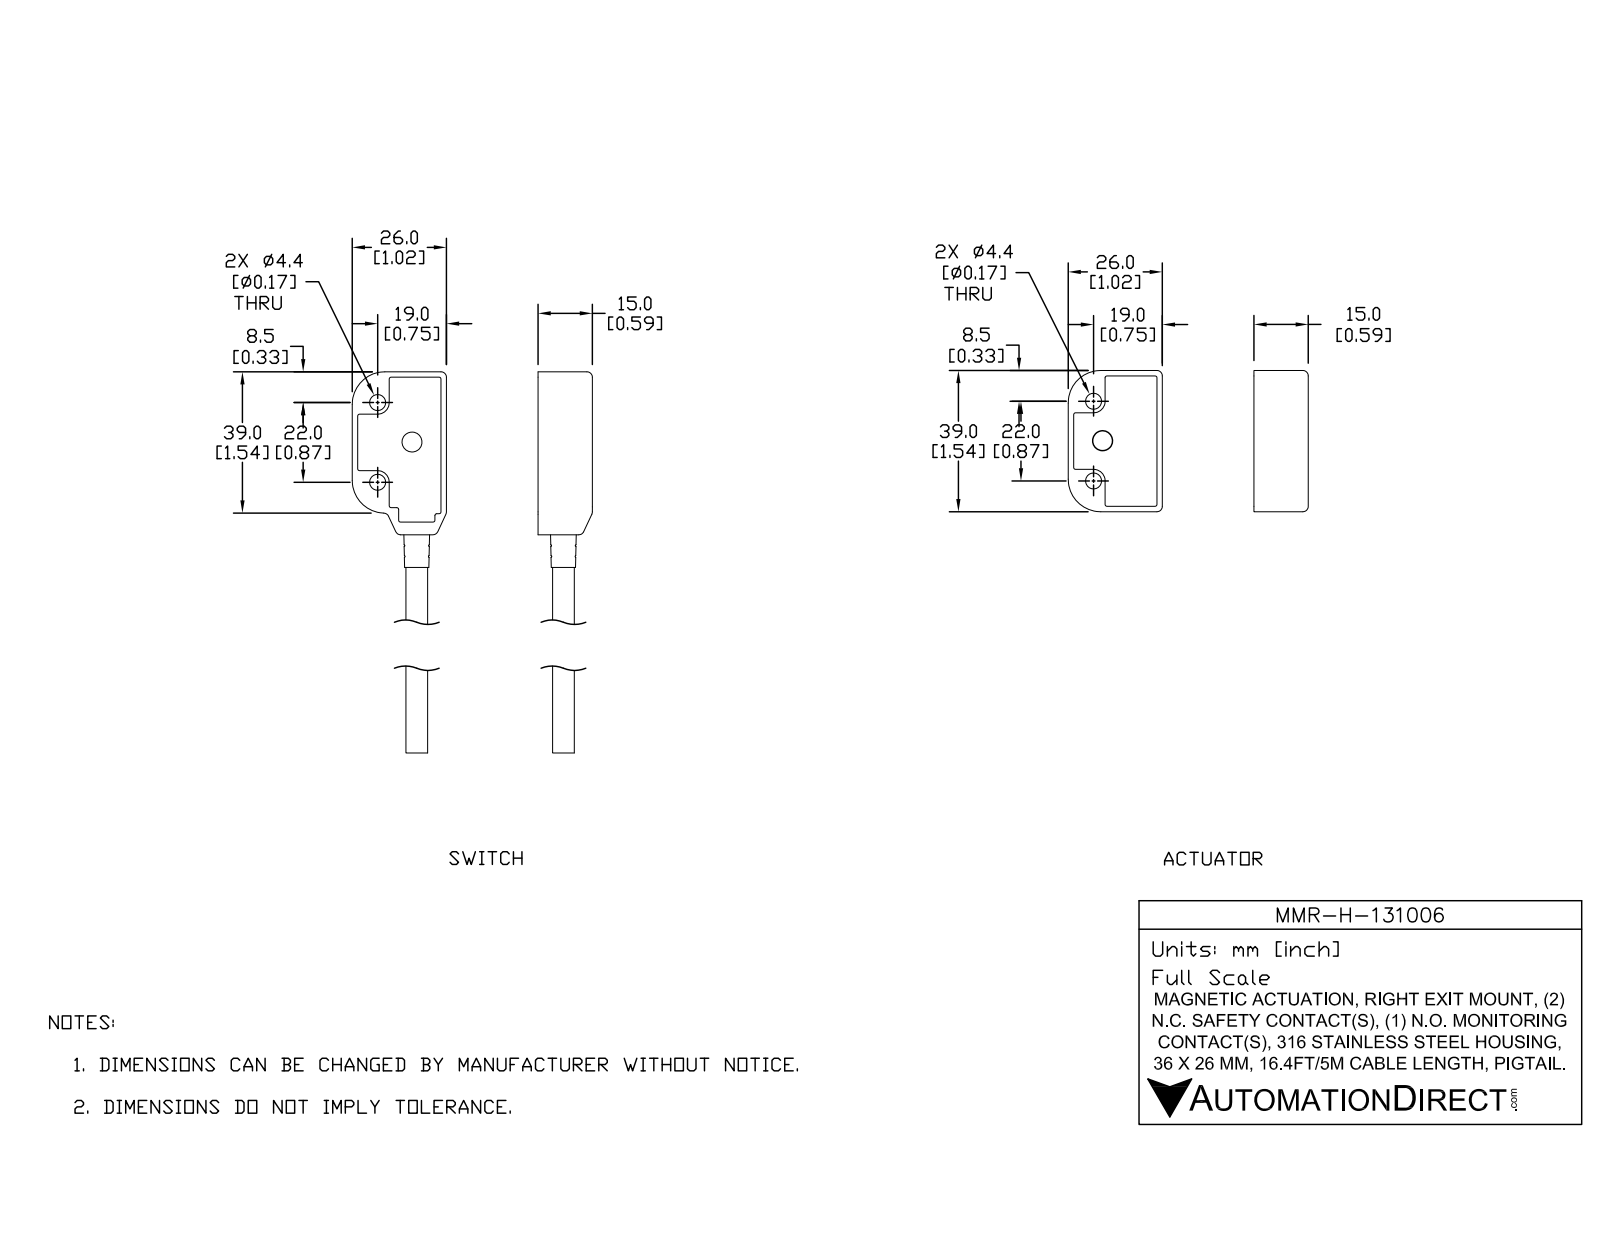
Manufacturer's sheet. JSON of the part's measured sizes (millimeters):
{"part_name": "MMR-H-131006; MMR-H-131006_2; MMR-H-131006_1", "step_written_by": "SolidWorks 2017 (AUTOMOTIVE_DESIGN)", "units": "millimeters", "bodies": {"solids": 7, "faces": 584, "planar": 173, "cylindrical": 224, "other": 187}, "overall_size": [198.2, 53, 15], "volume_mm3": 20190, "surface_area_mm2": 19520, "round_holes": [[4.4, 4], [5, 2], [5.9, 1], [7.2, 1]], "round_bosses_or_shafts": [[2, 2], [8.6, 1], [7.6, 1], [7.1, 1], [6, 1], [3, 1]], "partial_cylinders_radius": [[0.5, 82], [0.3, 26], [1.5, 15], [0.2, 8], [4, 6], [3.2, 4], [3.3, 4], [4.6, 4]], "face_to_face_distances": [1.5, 14.6, 13.1, 11.7, 2.5, 13.2, 1.4, 15, 13.5, 24.5], "hole_center_spacings": [22, 39, 44.8, 11.2, 11.4, 14.5, 14.6, 27]}
